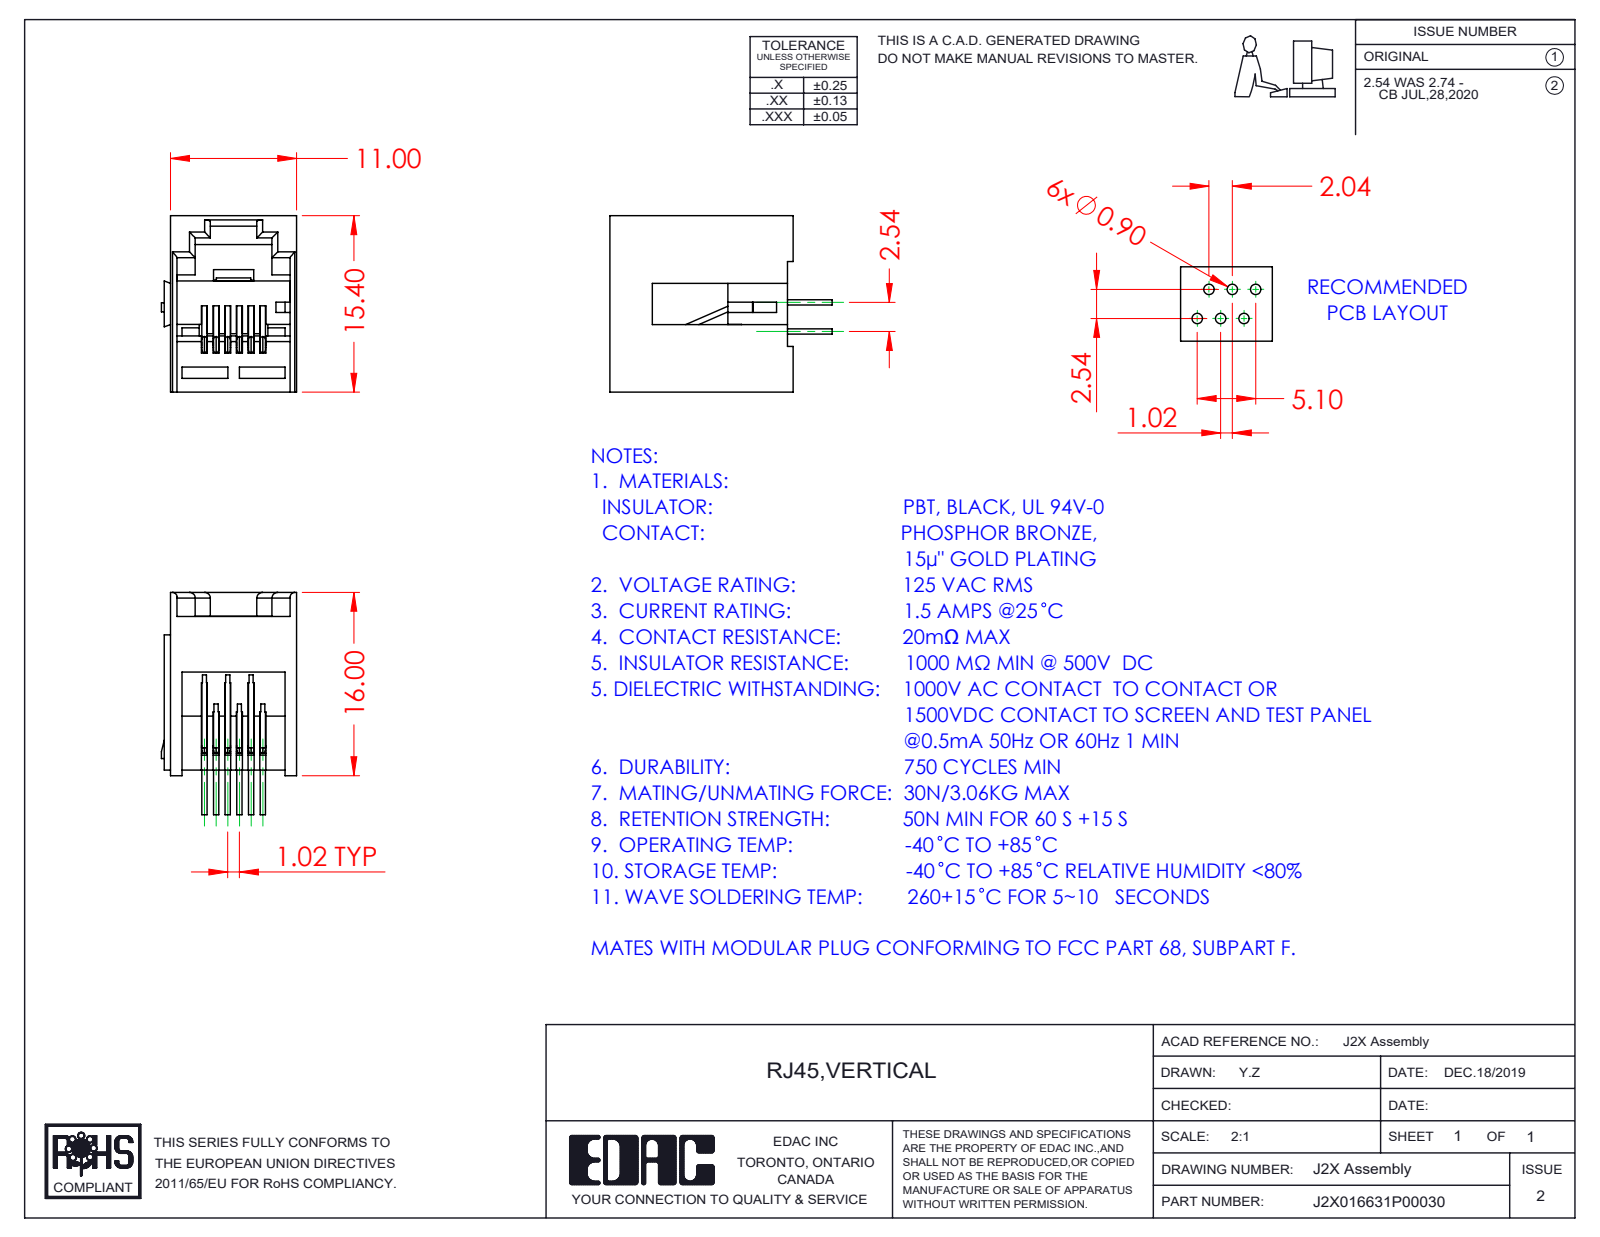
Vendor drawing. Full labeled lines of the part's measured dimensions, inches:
Part name (STEP PRODUCT): 2X Contact Lock; 2X Insulator; 2X Contacts_6P6C; J2X016631P00030
STEP written by: SolidWorks 2020 (CONFIG_CONTROL_DESIGN)
Units: inches
Bodies: 8 solids, 466 faces (333 planar, 97 cylindrical, 36 other)
Overall size (bounding box): 0.764 × 0.606 × 0.465
Volume: 0.074 in³ · Surface area: 4.408 in²
Round bosses / shafts (diameter × count): ⌀0.018 ×24
Partial cylindrical surfaces — rounded edges, fillets, slot ends (radius × count): R0.02 ×7, R0.006 ×2, R0.012 ×2, R0.016 ×2, R0.008 ×1
Main face-to-face distances: 0.039, 0.433, 0.08, 0.04, 0.02, 0.022, 0.02, 0.394, 0.472, 0.411
